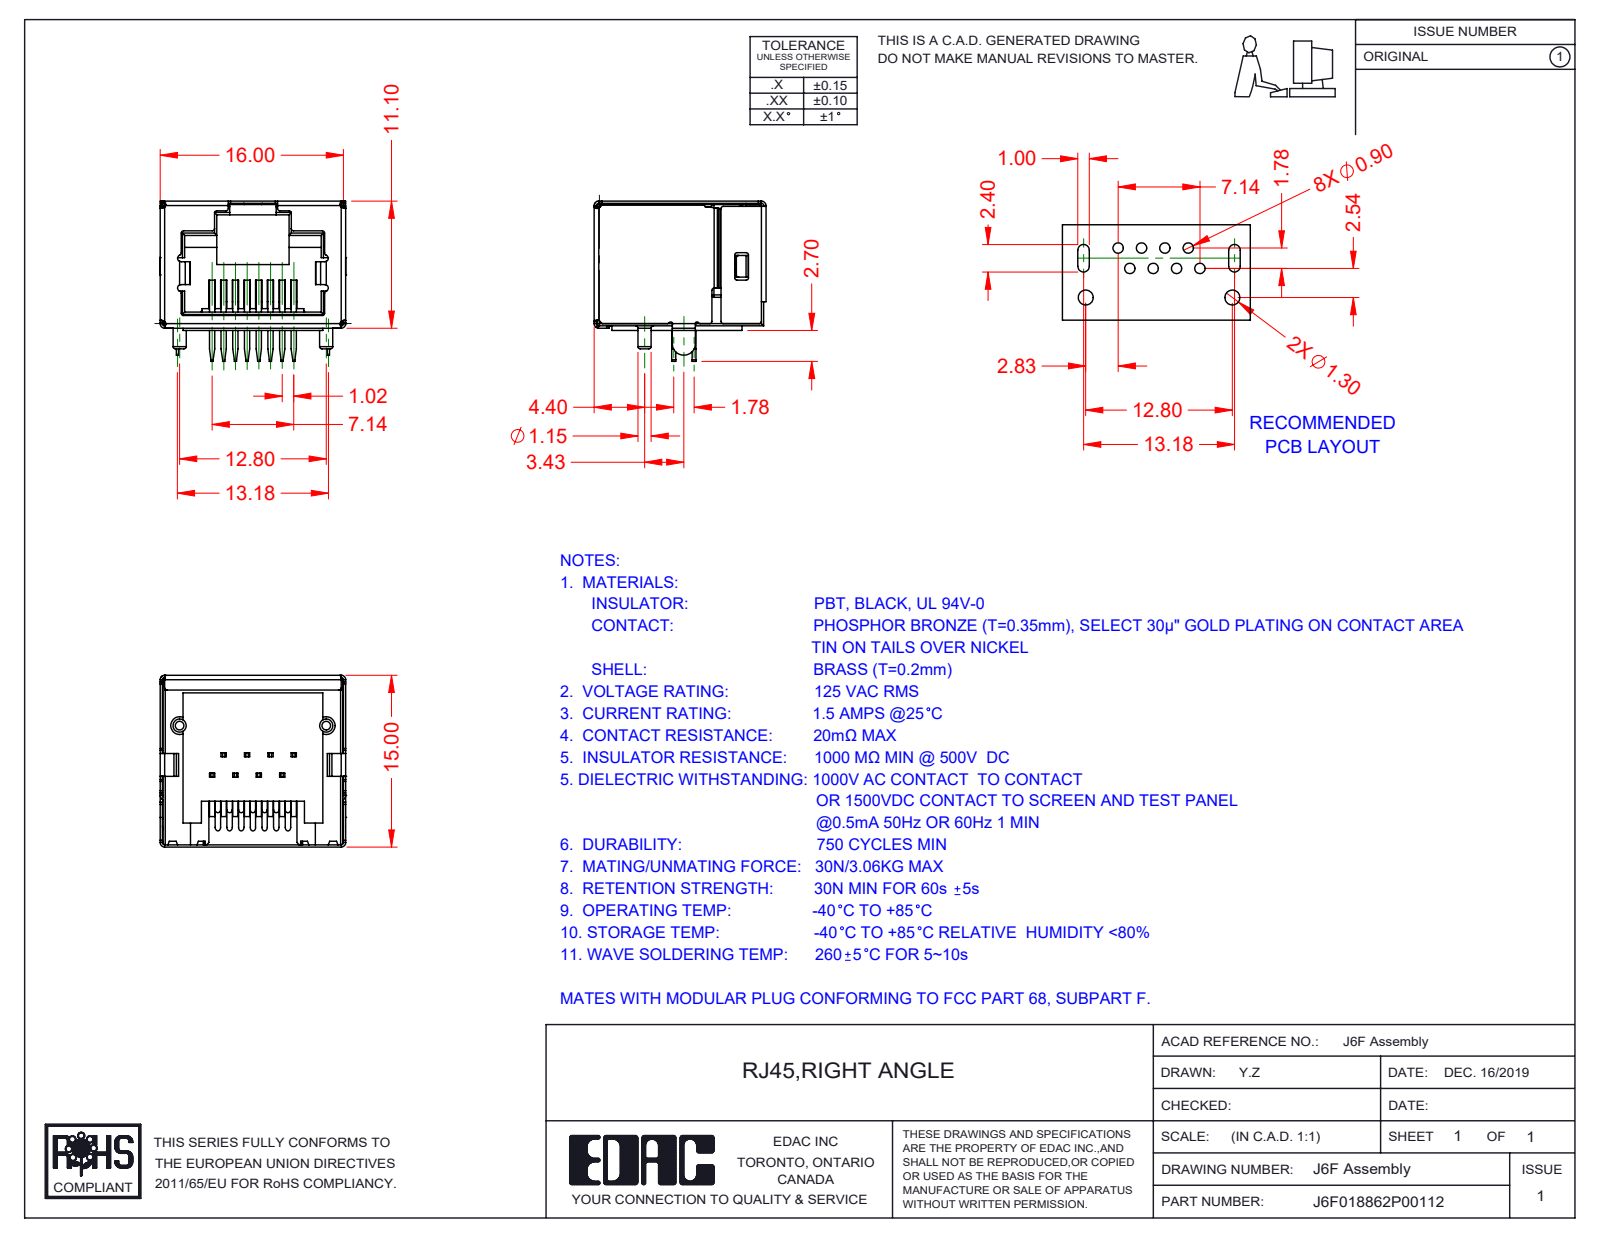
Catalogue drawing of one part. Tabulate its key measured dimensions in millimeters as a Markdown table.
| quantity | value |
| --- | --- |
| part name | 6F Contacts; 6F Insulator; 6F Shield; J6F018862P00112 |
| STEP written by | SolidWorks 2016 (CONFIG_CONTROL_DESIGN) |
| units | millimeters |
| bodies | 10 solids, 960 faces (695 planar, 223 cylindrical, 42 other) |
| overall size | 16.2 × 15 × 14 |
| volume | 1 336 mm³ |
| surface area | 3 711 mm² |
| round bosses / shafts (diameter × count) | 1.15 × 2 |
| partial cylindrical surfaces (radius × count) | 0.2 × 77, 0.4 × 24, 0.3 × 20, 0.5 × 9, 0.23 × 7, 0.15 × 5, 0.1 × 4, 1 × 3 |
| main face-to-face distances | 15.75, 16, 15.95, 11, 15.7, 9.7, 11.1, 16.2, 15.8, 1.2 |
